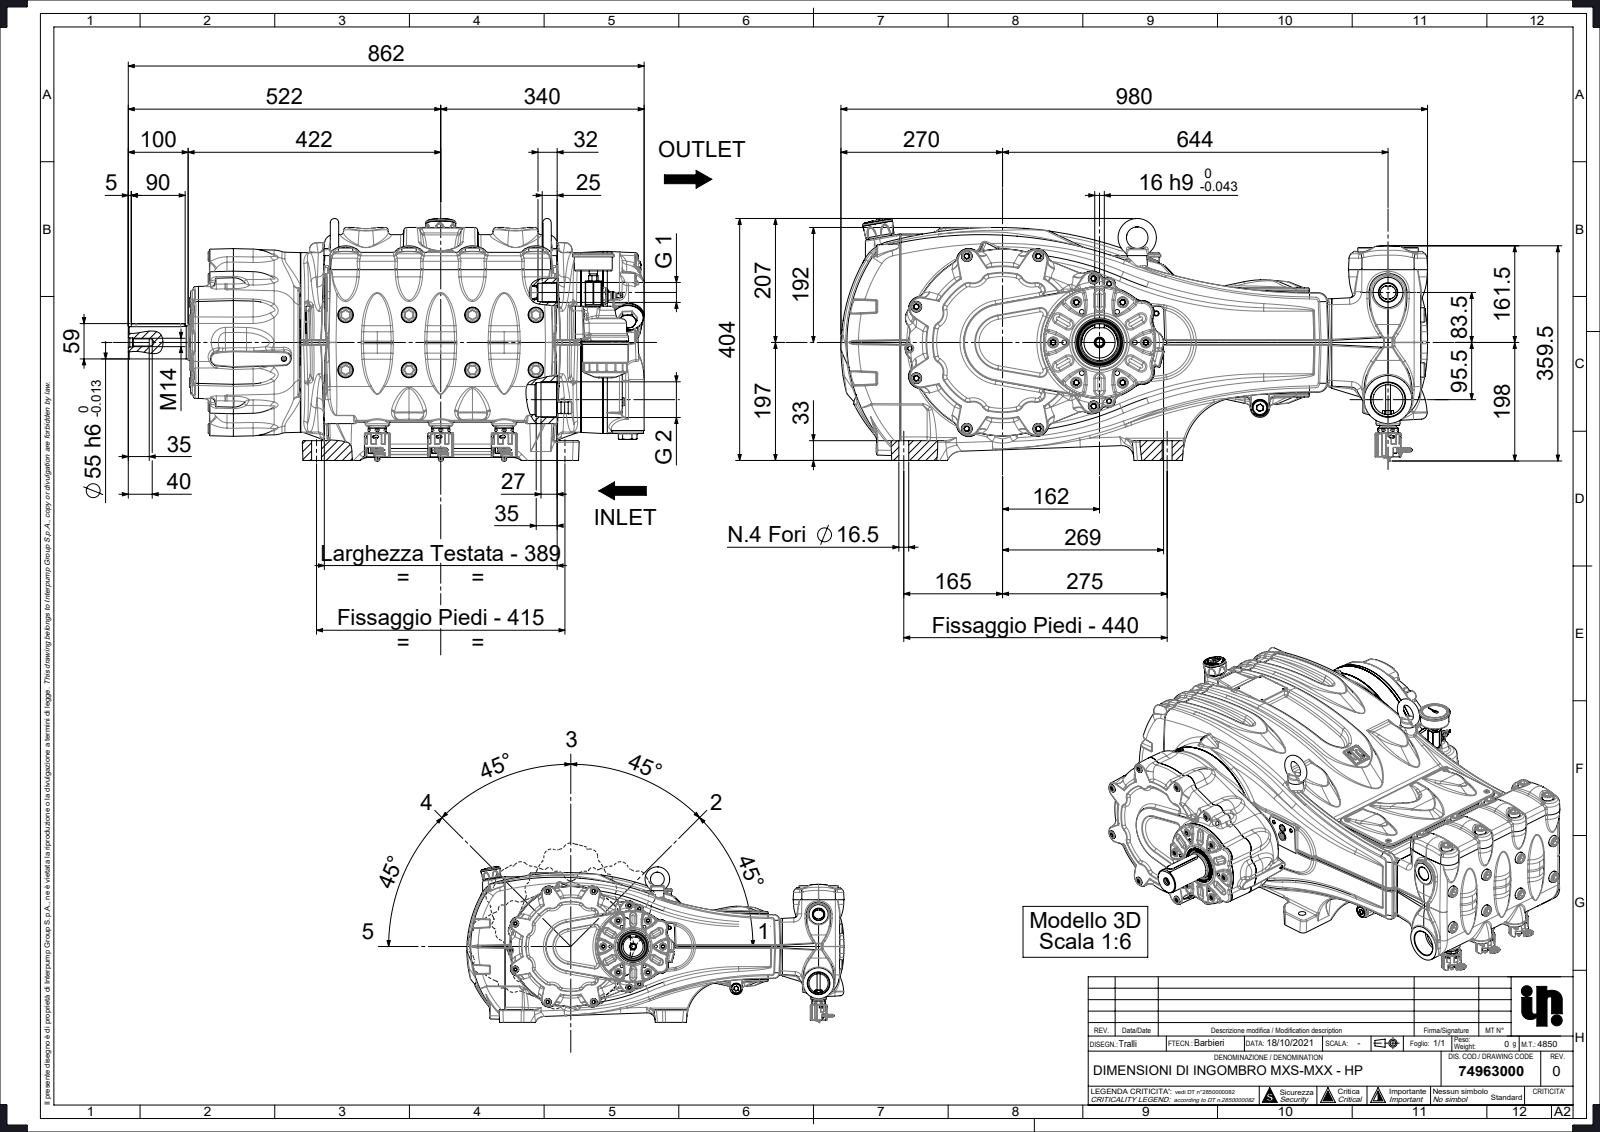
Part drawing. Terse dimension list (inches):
name: 1450112090-00012124; step mxs hp; 9000630002-00020642; IP-74218284-00039343 (+8 more)
written by: SolidWorks 2020 (AUTOMOTIVE_DESIGN)
unit: in
bodies: 141 solids, 15986 faces (2713 planar, 3844 cylindrical, 9429 other)
size: 38.587 × 34.036 × 15.941
volume: 7 829 in³; area: 7 767 in²
holes: 35× ⌀0.551, 28× ⌀0.669, 20× ⌀0.354, 14× ⌀0.268, 14× ⌀0.512, 13× ⌀0.197, 11× ⌀0.787, 10× ⌀0.335, 10× ⌀0.413, 10× ⌀0.65, 9× ⌀0.984, 8× ⌀0.315
bosses: 34× ⌀0.63, 30× ⌀0.315, 26× ⌀0.512, 20× ⌀0.394, 16× ⌀0.945, 10× ⌀0.709, 9× ⌀0.472, 8× ⌀1.417
rounds: 532× R0.02, 156× R0.012, 116× R0.079, 99× R0.059, 87× R0.197, 83× R0.008, 65× R0.315, 62× R0.118
face distances: 0.016, 24.594, 18.441, 4.425, 20.169, 4.409, 20.184, 6.378, 1.594, 7.972
hole spacings: 9.7, 0.906, 4.343, 7.515, 4.173, 1.811, 3.315, 4.055
